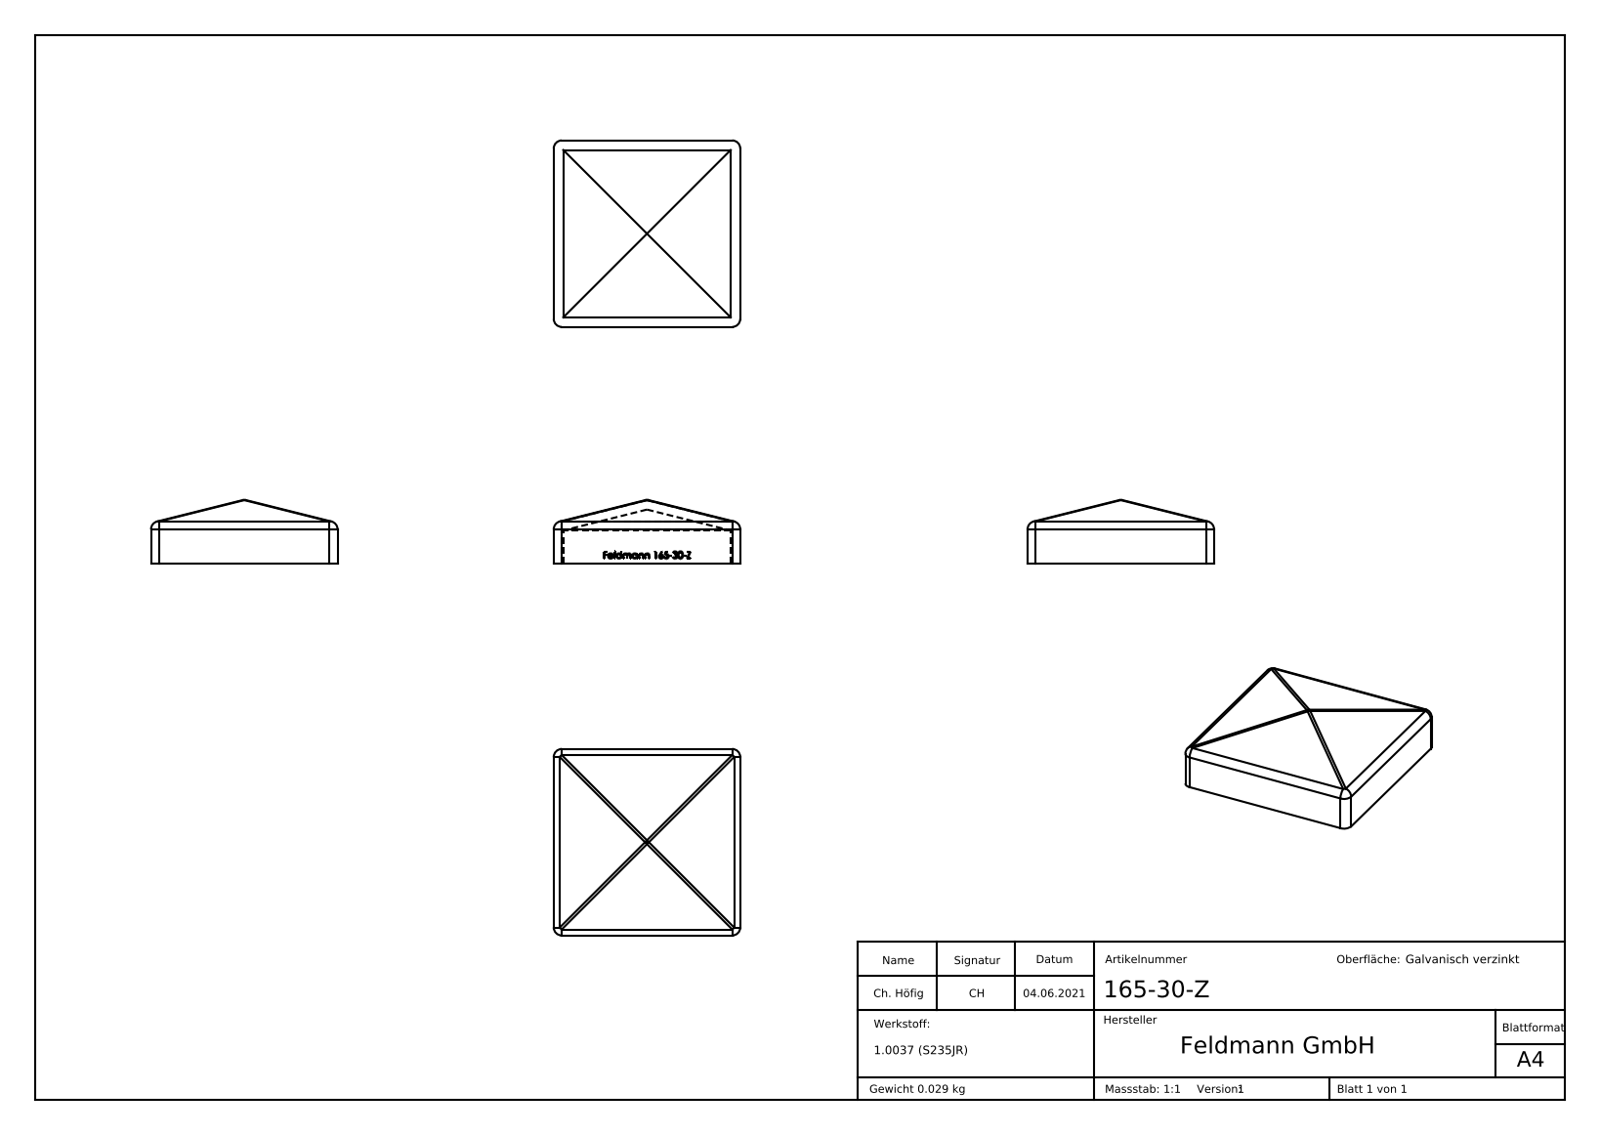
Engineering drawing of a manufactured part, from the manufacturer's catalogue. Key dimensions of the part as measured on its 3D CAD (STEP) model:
Part name (STEP PRODUCT): 165-30-Z
STEP written by: SolidWorks 2018 (CONFIG_CONTROL_DESIGN)
Units: millimetres
Bodies: 1 solid, 234 faces (126 planar, 12 cylindrical, 96 other)
Overall size (bounding box): 35 × 35 × 12
Volume: 3 664 mm³ · Surface area: 4 314 mm²
Partial cylindrical surfaces — rounded edges, fillets, slot ends (radius × count): R1.5 ×12
Main face-to-face distances: 1.8, 33.2, 35, 31.4, 1.7, 31.5, 33.3, 9.7, 1, 1.32
